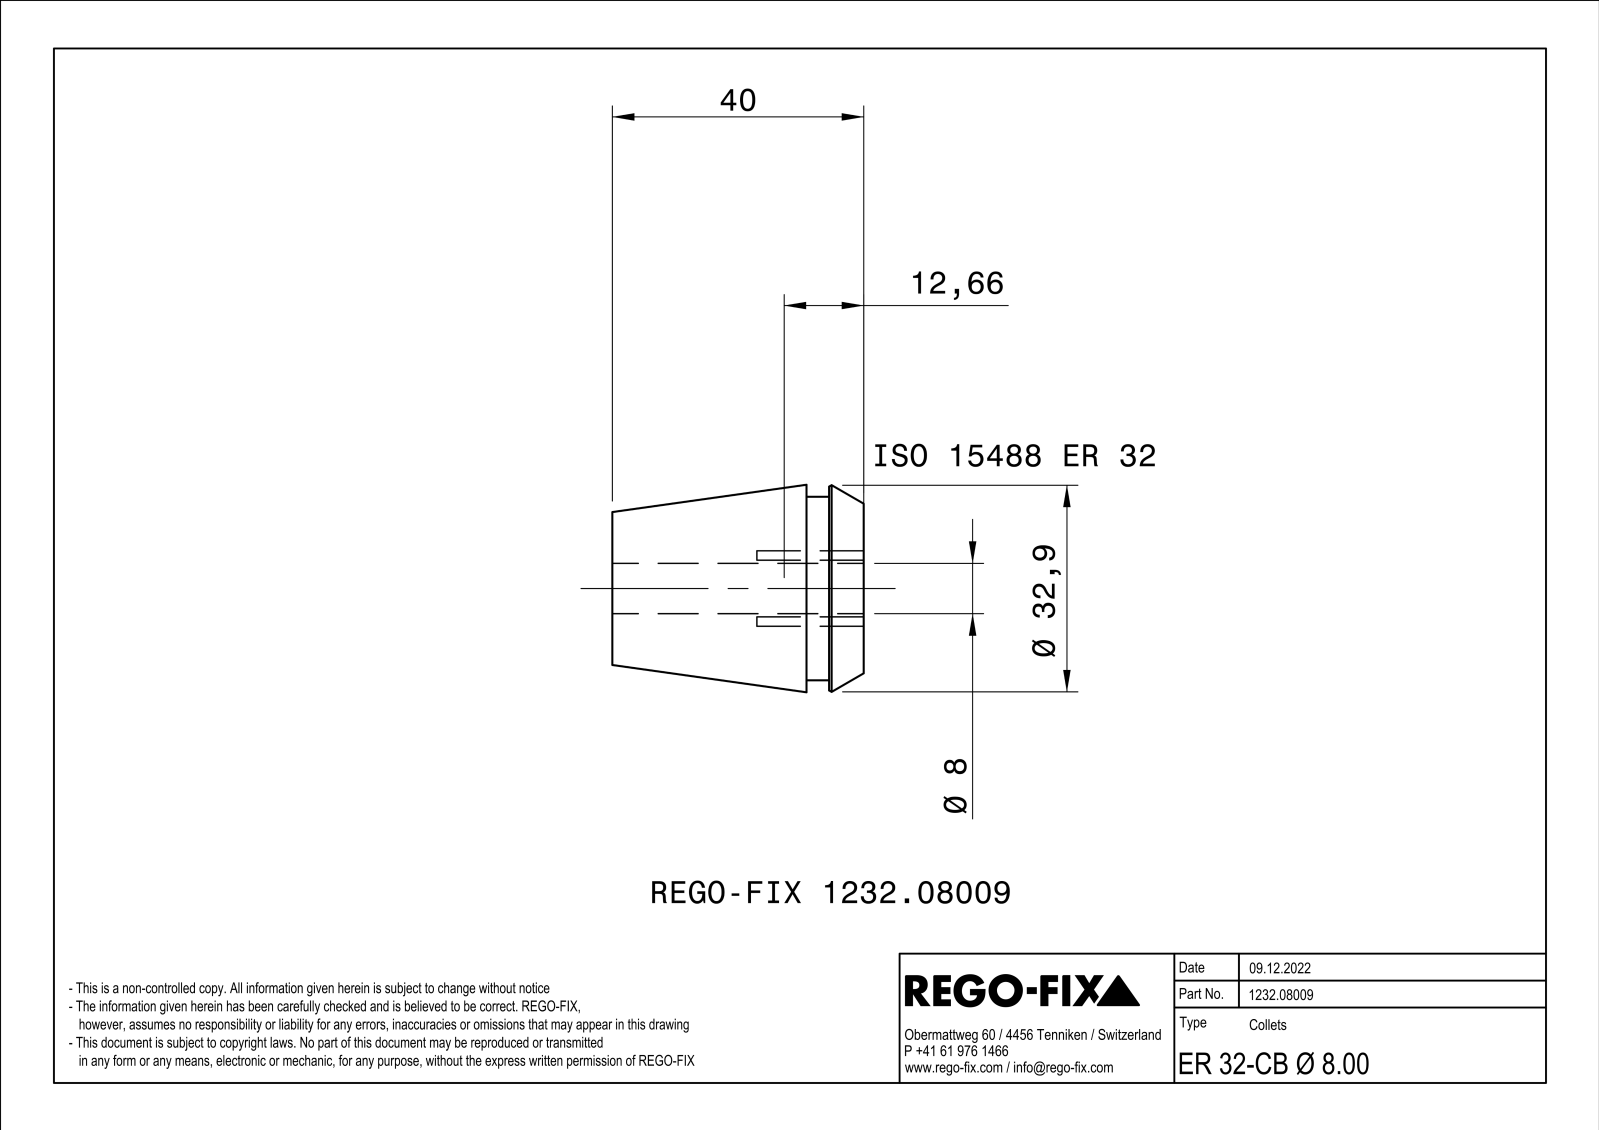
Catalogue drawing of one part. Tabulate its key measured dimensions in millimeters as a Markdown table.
| quantity | value |
| --- | --- |
| part name | NOCUT |
| STEP written by | SIEMENS PLM Software Solid Edge ST10 (AUTOMOTIVE_DESIGN) |
| units | millimeters |
| bodies | 1 solid, 178 faces (64 planar, 21 cylindrical, 93 other) |
| overall size | 40 × 32.99 × 32.99 |
| volume | 20 380 mm³ |
| surface area | 15 281 mm² |
| round holes (diameter × count) | 1.5 × 4, 8 × 1 |
| round bosses / shafts (diameter × count) | 33 × 1, 29.2 × 1 |
| main face-to-face distances | 0.8, 40, 5.5, 34.5, 9.1, 3.6, 30.9 |
| hole center spacings | 5.25, 7.42, 10.5 |
